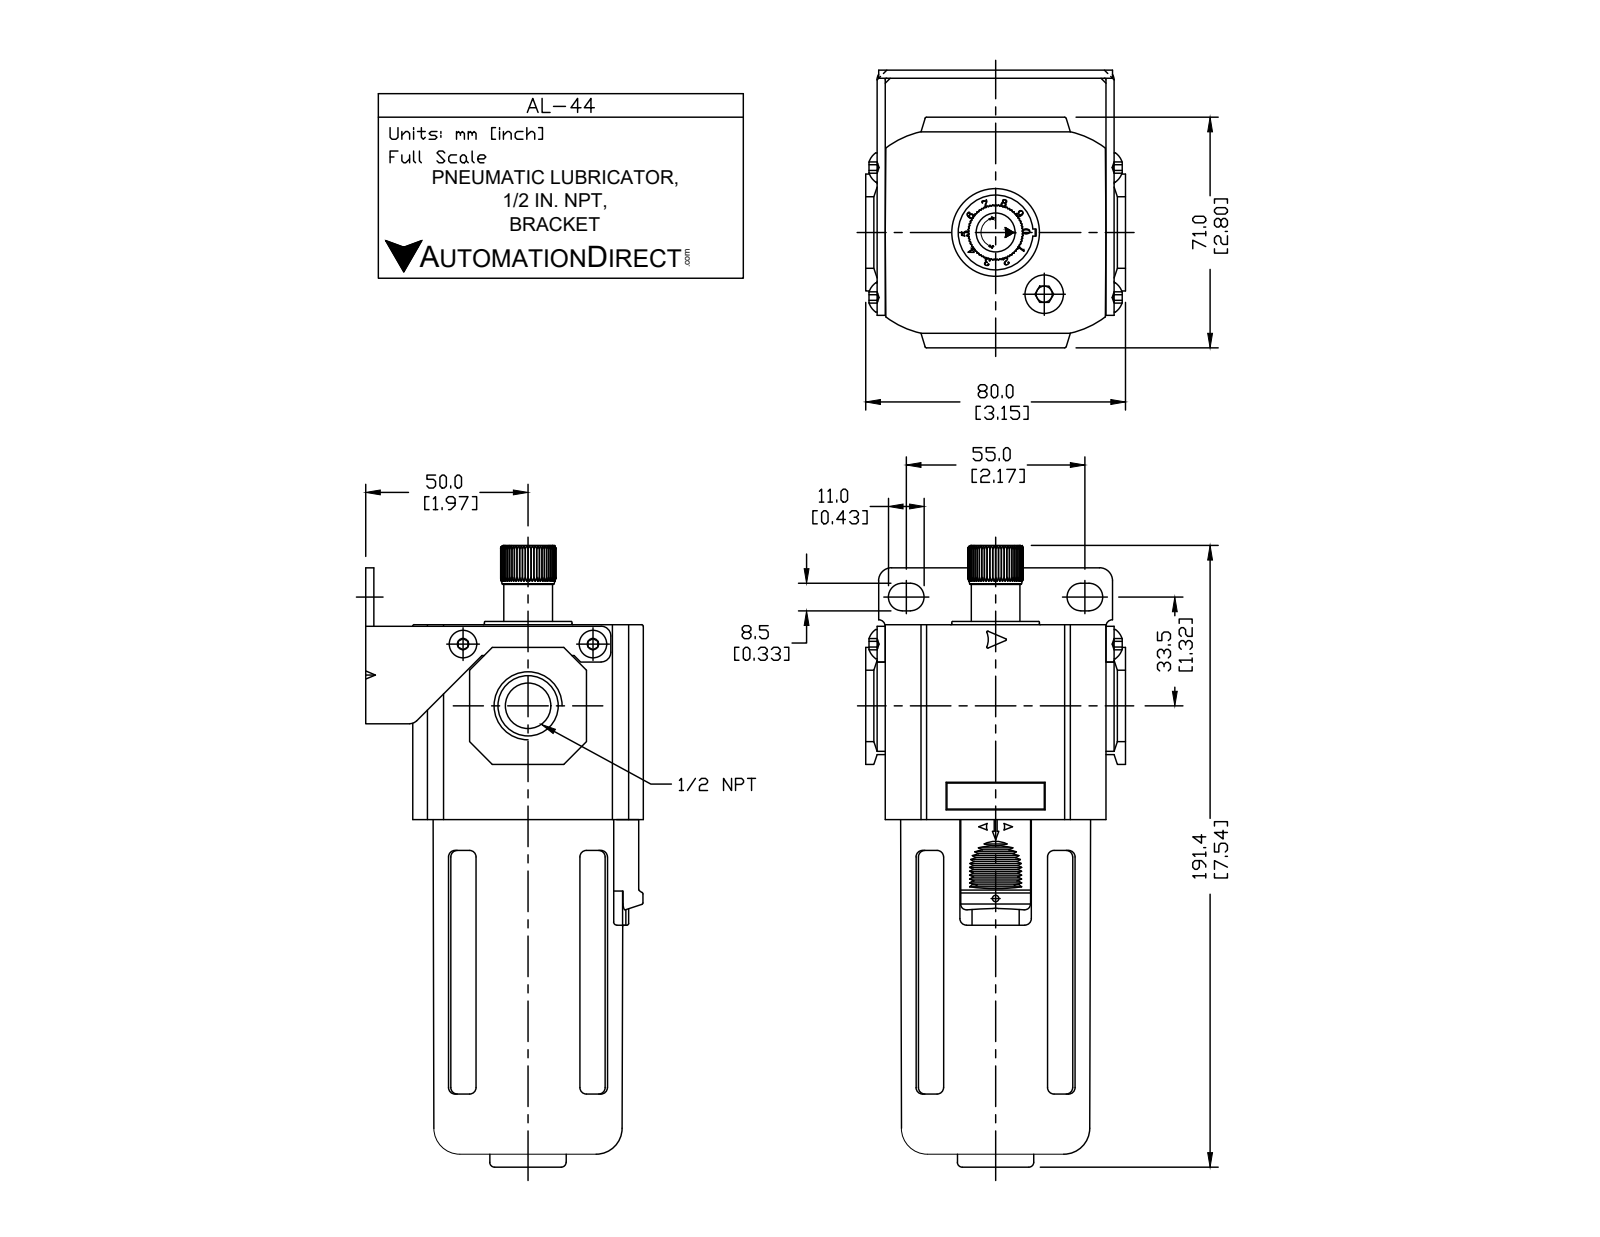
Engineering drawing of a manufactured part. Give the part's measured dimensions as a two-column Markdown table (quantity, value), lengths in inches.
| quantity | value |
| --- | --- |
| part name | AL-44 |
| STEP written by | SolidWorks 2015 (CONFIG_CONTROL_DESIGN) |
| units | inches |
| bodies | 7 solids, 550 faces (336 planar, 106 cylindrical, 108 other) |
| overall size | 7.461 × 3.366 × 3.15 |
| volume | 23.38 in³ |
| surface area | 138 in² |
| round holes (diameter × count) | 0.134 × 2, 0.703 × 1, 1.969 × 1, 2.351 × 1 |
| round bosses / shafts (diameter × count) | 2.302 × 1, 1.315 × 1, 1.024 × 1, 0.925 × 1, 0.591 × 1 |
| partial cylindrical surfaces (radius × count) | 0.039 × 18, 0.079 × 8, 0.012 × 4, 0.167 × 4, 0.787 × 4, 0.008 × 3, 0.118 × 2, 0.177 × 2 |
| main face-to-face distances | 0.098, 3.268, 3.366, 0.571, 0.472, 2.795, 2.776, 2.677, 2.098, 3.012 |
| hole center spacings | 1.086, 1.575 |
